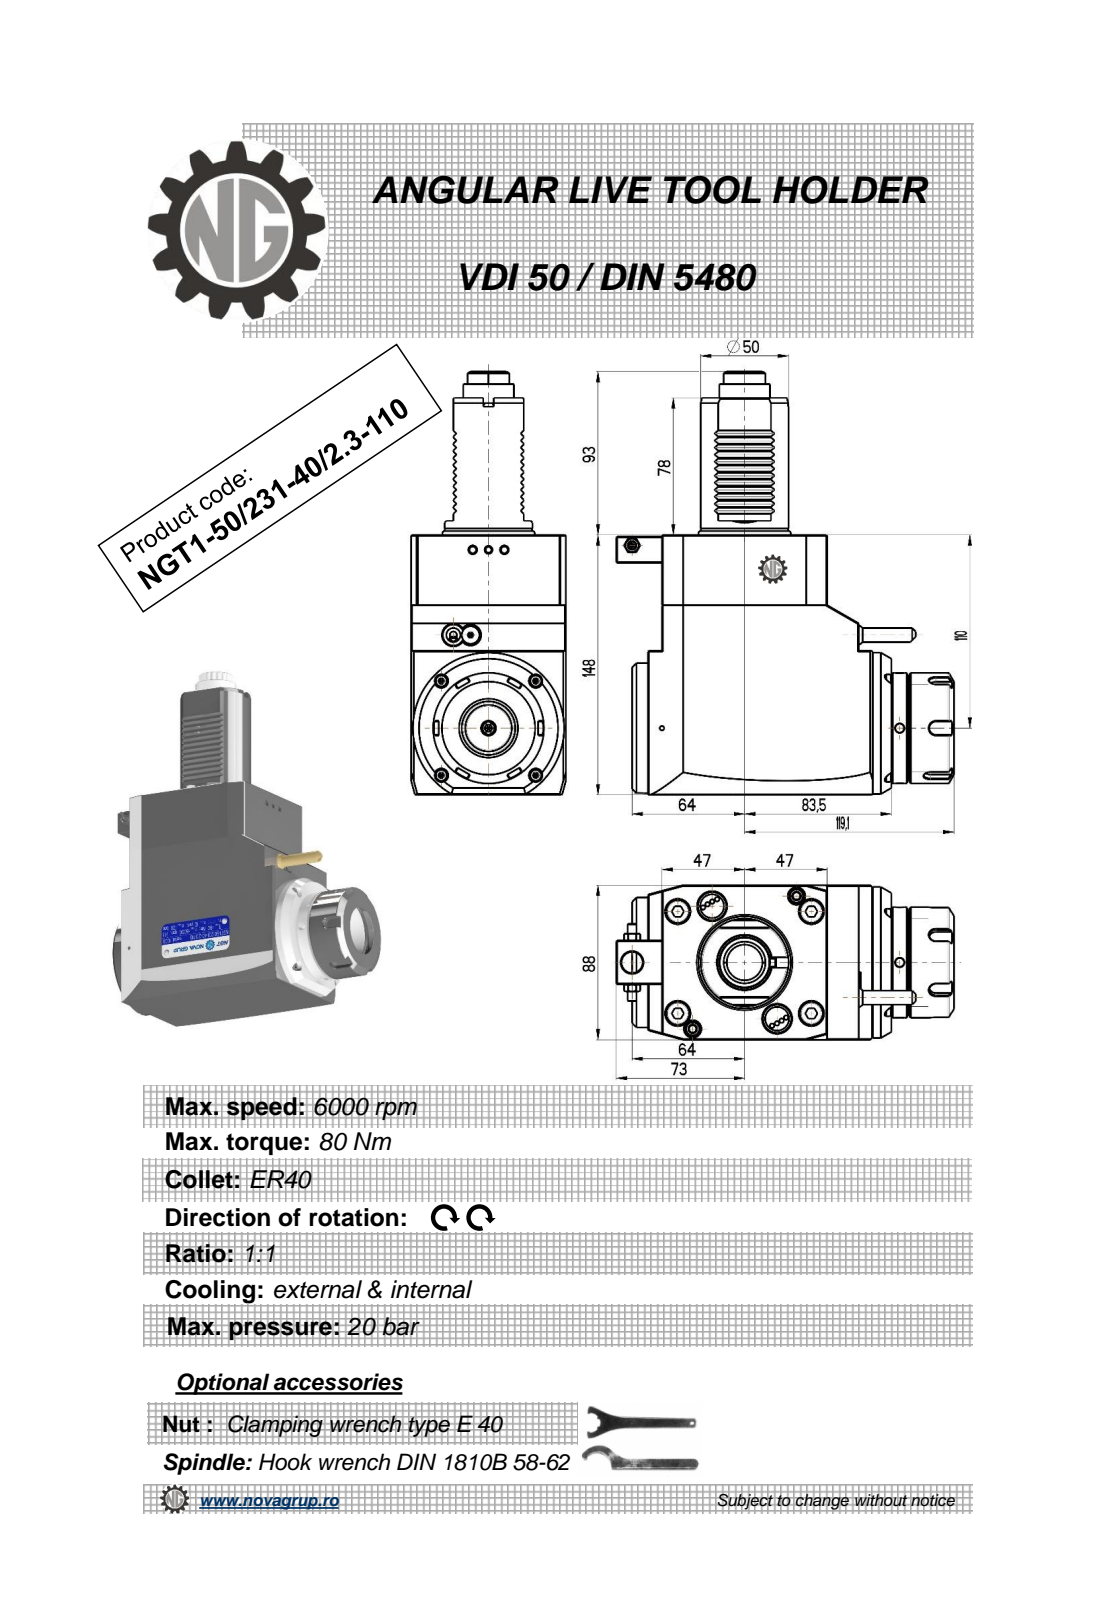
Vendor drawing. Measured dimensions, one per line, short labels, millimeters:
name: NGT1_50_231_40_1_3_110
written by: PRO/ENGINEER BY PARAMETRIC TECHNOLOGY CORPORATION, 2010280 (CONFIG_CONTROL_DESIGN)
unit: mm
bodies: 1 solid, 573 faces (247 planar, 173 cylindrical, 153 other)
size: 241 × 192.1 × 88
volume: 1 833 000 mm³; area: 114 886 mm²
holes: 3× ⌀5, 1× ⌀3, 1× ⌀4.2, 1× ⌀9.5, 1× ⌀12, 1× ⌀33.5
bosses: 1× ⌀86, 1× ⌀74, 1× ⌀63, 1× ⌀51, 1× ⌀50, 1× ⌀28.8, 1× ⌀10, 1× ⌀8.96
rounds: 36× R3.04, 24× R0.3, 12× R0.26, 6× R0.2, 5× R3.75, 1× R10.56, 1× R11.88, 1× R17.5
face distances: 88, 148, 94, 147.5, 17, 8, 9, 111, 120, 36.5
hole spacings: 52.46, 56.65, 101.5, 152.25, 184.38
